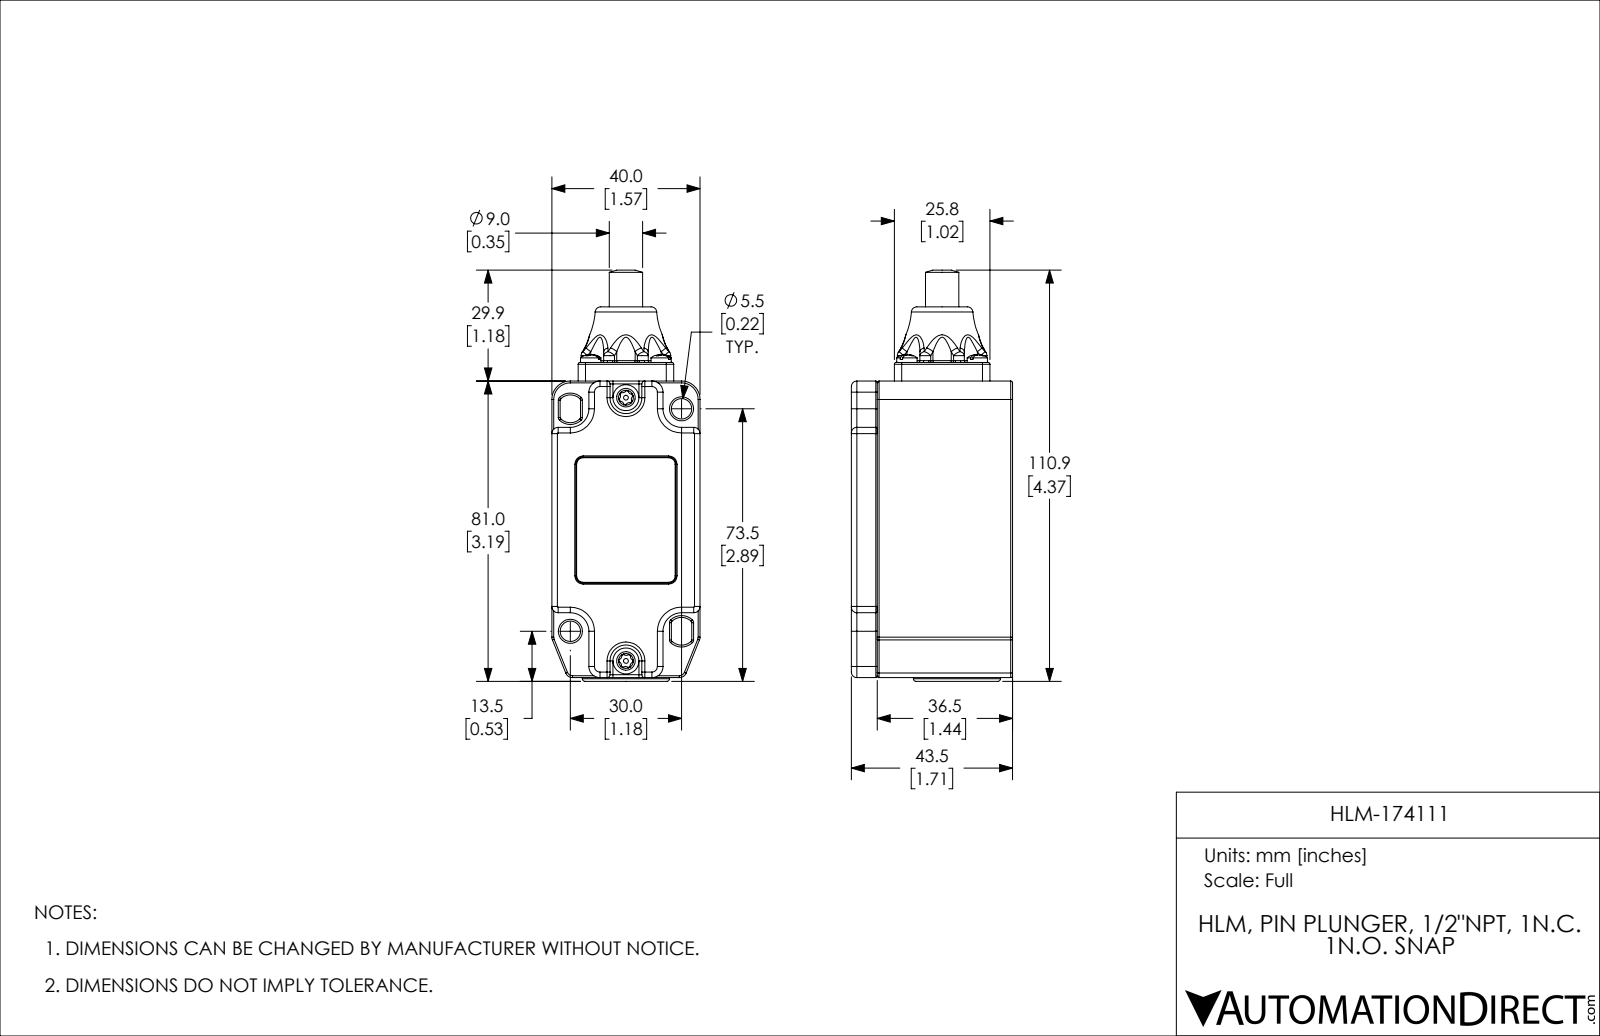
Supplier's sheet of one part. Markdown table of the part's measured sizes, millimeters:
| quantity | value |
| --- | --- |
| part name | 174-HLM (Pin Plunger) step format |
| STEP written by | SolidWorks 2013 (CONFIG_CONTROL_DESIGN) |
| units | millimeters |
| bodies | 12 solids, 2070 faces (508 planar, 583 cylindrical, 979 other) |
| overall size | 110.9 × 43.5 × 40 |
| volume | 60 553 mm³ |
| surface area | 43 836 mm² |
| round holes (diameter × count) | 3 × 10, 3.3 × 4, 3.7 × 2, 3.8 × 2, 4 × 2, 4.2 × 2, 5.5 × 2, 3.5 × 1, 4.4 × 1, 5.6 × 1, 6.9 × 1, 9 × 1 |
| round bosses / shafts (diameter × count) | 6.2 × 6, 5.48 × 4, 7 × 2, 6.4 × 2, 1.3 × 2, 23.5 × 1, 18.5 × 1, 17.7 × 1 |
| partial cylindrical surfaces (radius × count) | 0.5 × 173, 0.4 × 26, 1 × 25, 0.15 × 14, 0.3 × 12, 1.7 × 12, 2 × 12, 0.8 × 10 |
| main face-to-face distances | 2.25, 37.75, 40, 2.5, 35.5, 38.4, 40.9, 4.4, 43.5, 41 |
| hole center spacings | 19, 13.44, 9, 10.98, 16.51, 19.04, 21.02, 21.69 |
